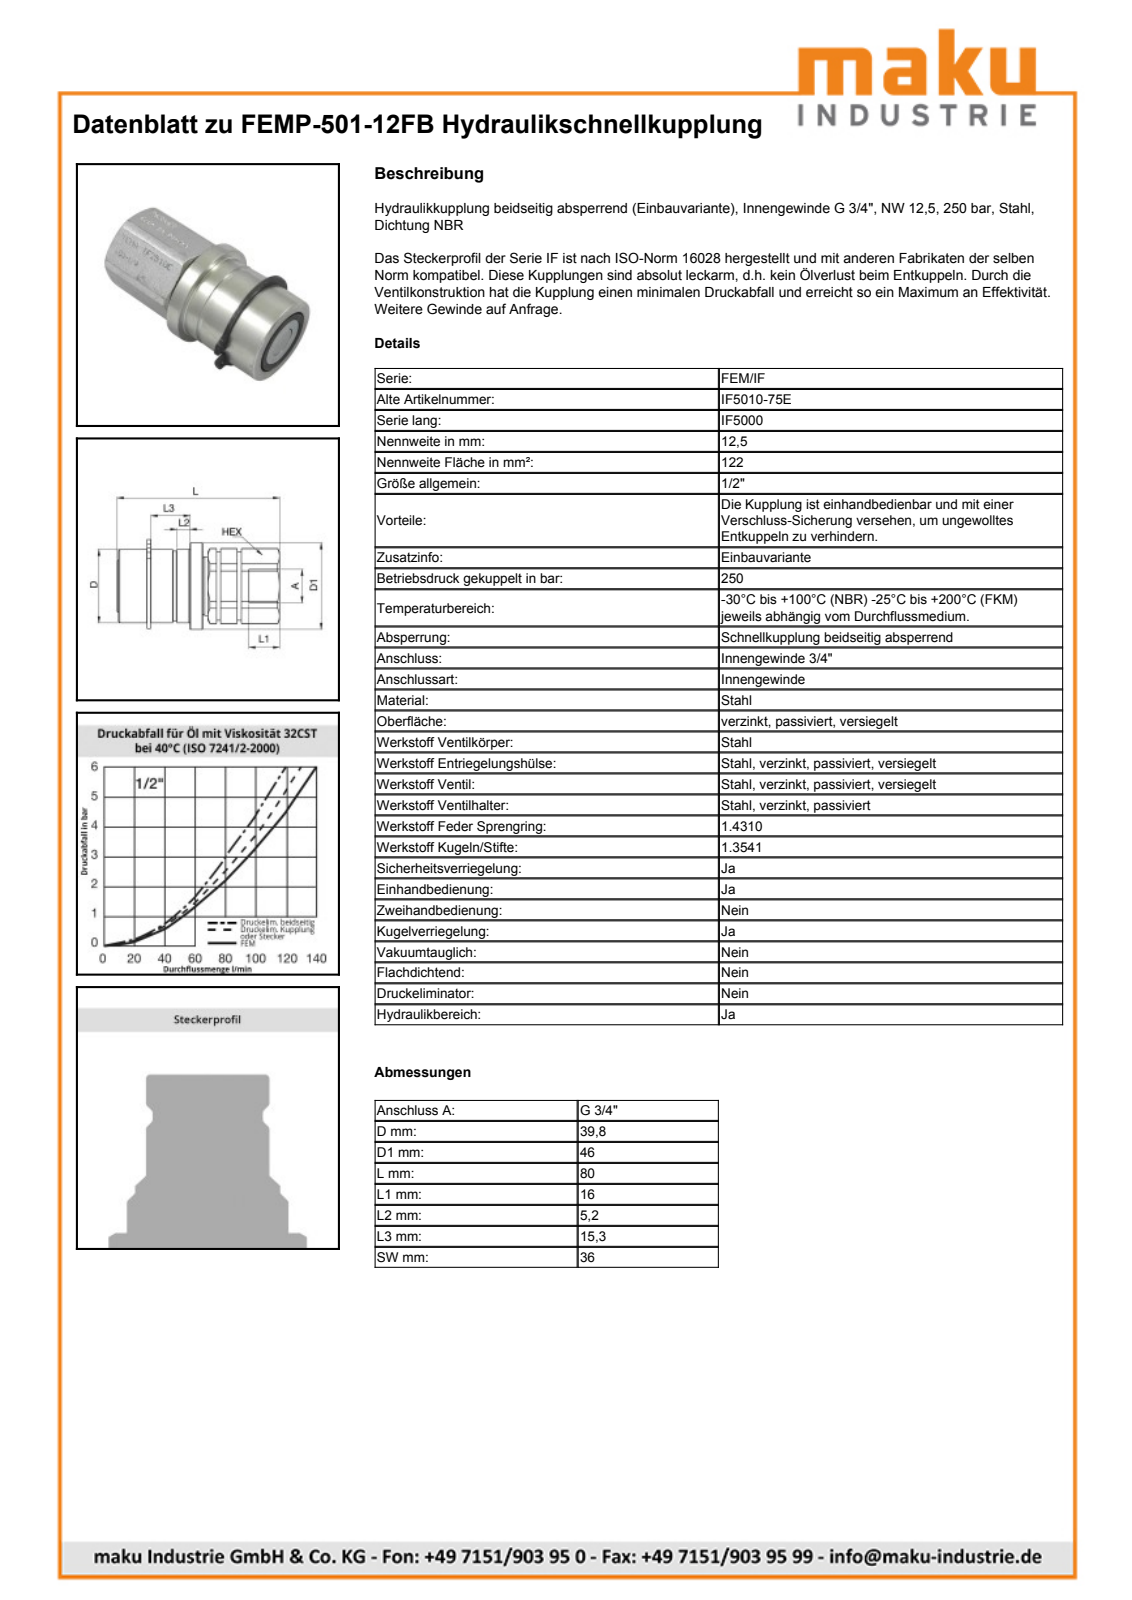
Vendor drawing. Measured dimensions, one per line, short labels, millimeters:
name: FEMP-501-12FB
written by: SolidWorks 2009 (AUTOMOTIVE_DESIGN)
unit: mm
bodies: 2 solids, 155 faces (32 planar, 61 cylindrical, 62 other)
size: 79.9 × 47.17 × 46
volume: 86 317 mm³; area: 18 306 mm²
holes: 2× ⌀2.5, 1× ⌀15.75, 1× ⌀24.12, 1× ⌀24.7, 1× ⌀31.6, 1× ⌀34.4, 1× ⌀35.8
bosses: 1× ⌀46, 1× ⌀40, 1× ⌀39.8, 1× ⌀37.5, 1× ⌀32.6, 1× ⌀31.42, 1× ⌀31.2, 1× ⌀30
rounds: 2× R3, 2× R7, 1× R21.75, 1× R24.23
face distances: 36, 17.98, 67.8, 49.82, 79.6, 61.62, 11.8, 66.2, 48.22, 1.6
hole spacings: 20.78, 10
